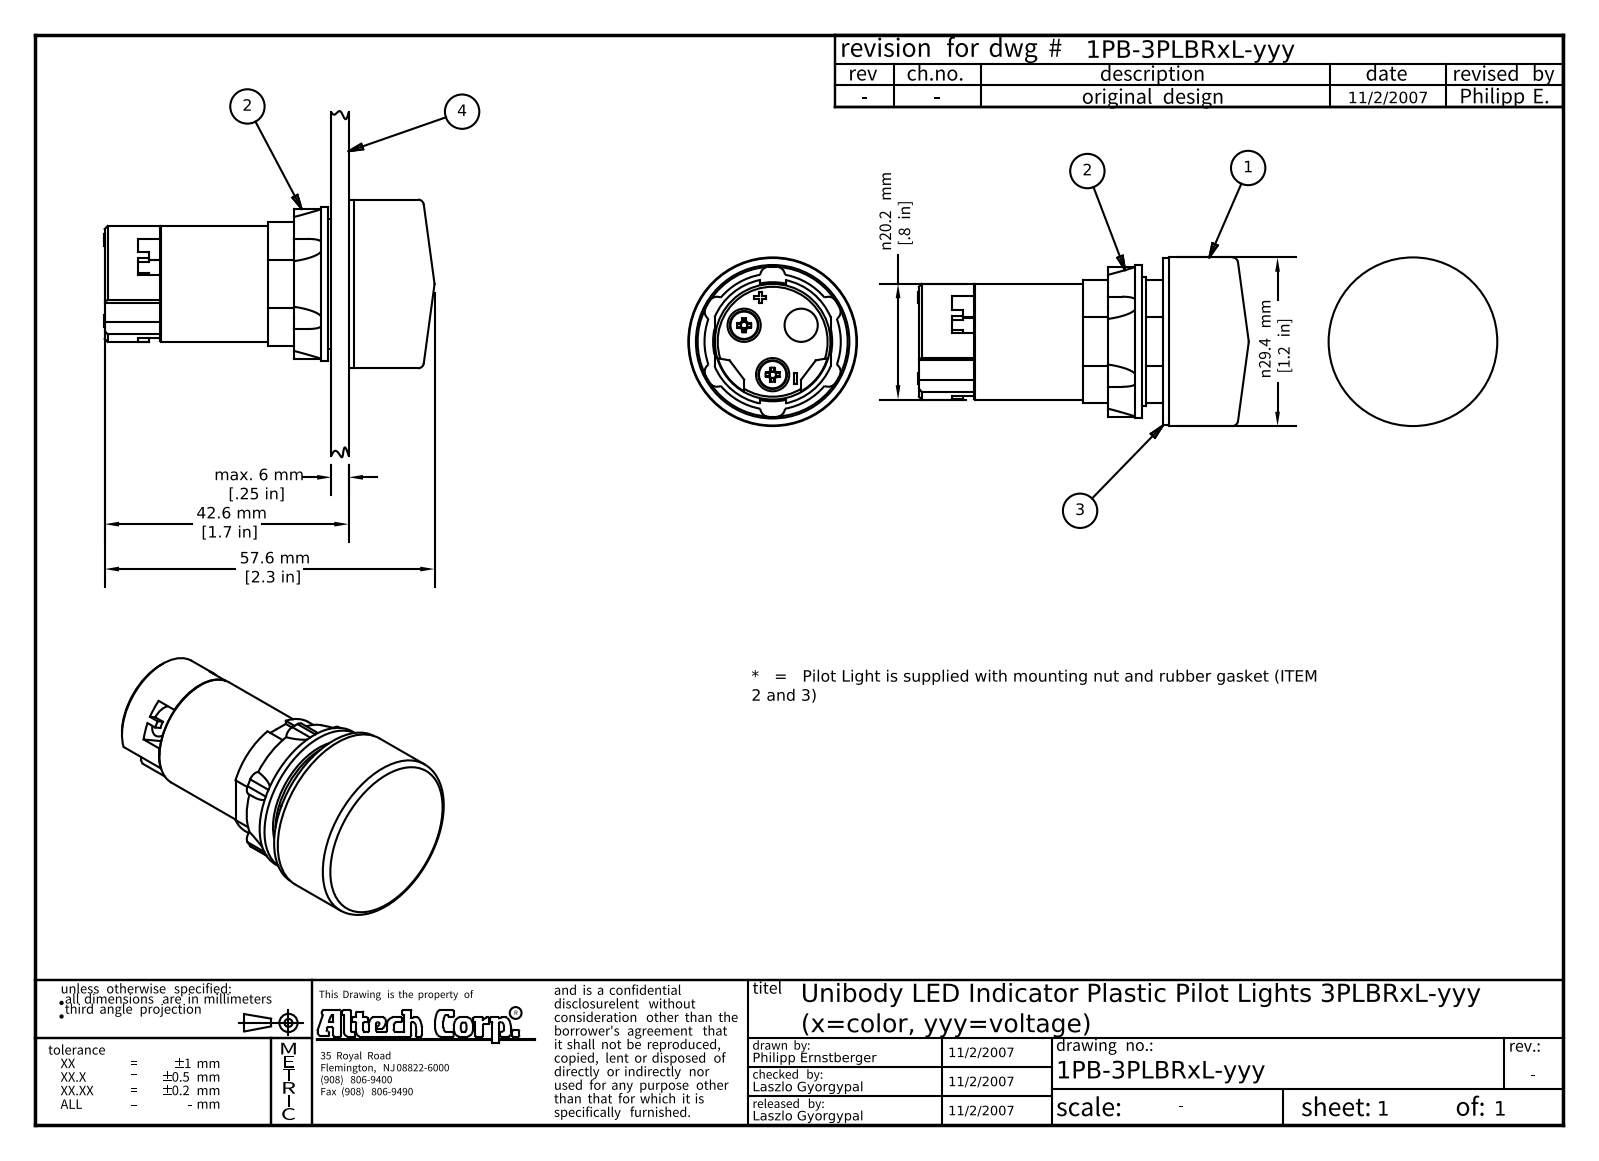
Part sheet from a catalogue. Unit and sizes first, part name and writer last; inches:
Units: inches
Overall size (bounding box): 2.38 × 2.272 × 1.772
Round holes (diameter × count): ⌀0.228 ×3, ⌀0.819 ×1, ⌀0.886 ×1
Round bosses / shafts (diameter × count): ⌀0.098 ×2, ⌀0.089 ×2, ⌀1.159 ×1, ⌀1.152 ×1, ⌀1.055 ×1, ⌀0.89 ×1, ⌀0.795 ×1, ⌀0.787 ×1
Partial cylindrical surfaces — rounded edges, fillets, slot ends (radius × count): R0.059 ×12, R0.433 ×1
Main face-to-face distances: 0.118, 0.486, 1.285, 1.559, 1.677, 1.772, 0.142, 1.535, 0.024, 1.303
Hole centre spacings: 0.226, 0.392
Volume: 1.841 in³ · Surface area: 20.77 in²
Bodies: 5 solids, 213 faces (131 planar, 36 cylindrical, 46 other)
Part name (STEP PRODUCT): 3PLBRxL-yyy_assemly; 3PLBRxL-xxx; P2MN; DIN 7985 (H) M2 (+1 more)
STEP written by: Autodesk Inventor 2008 (AUTOMOTIVE_DESIGN)
